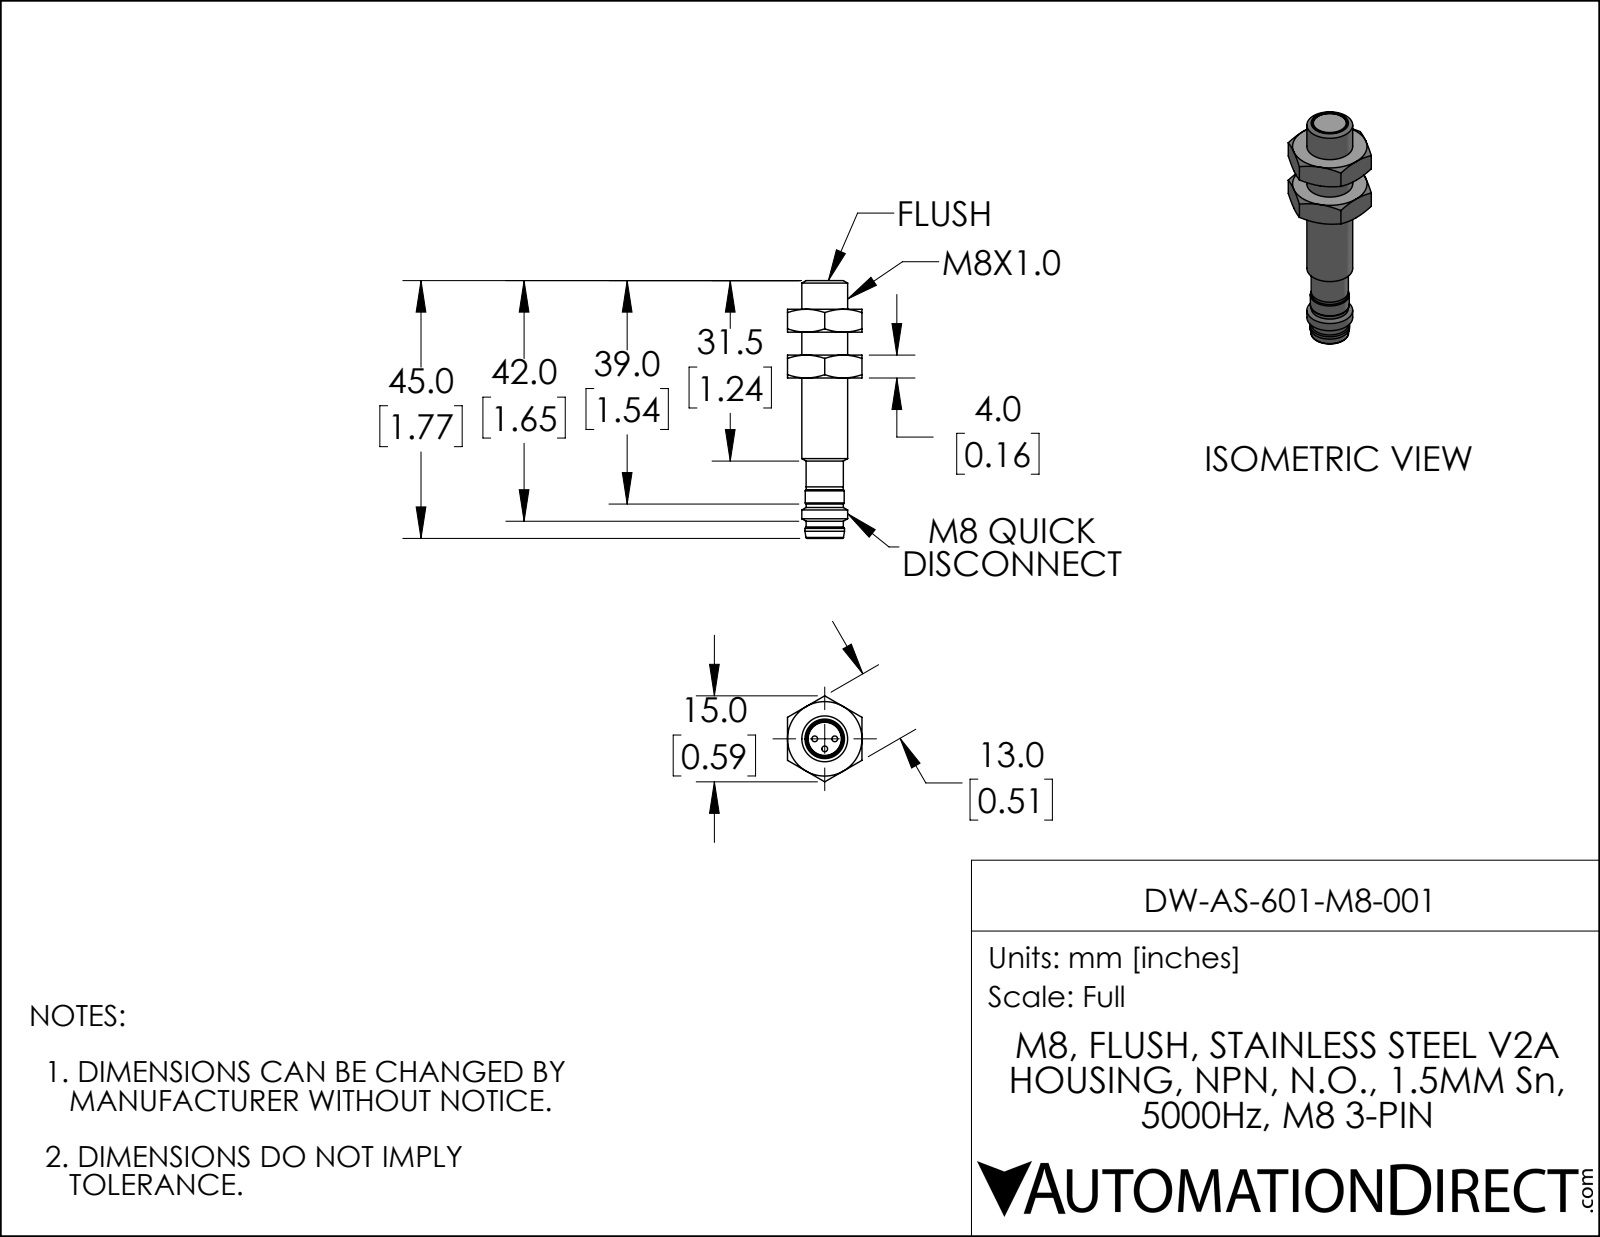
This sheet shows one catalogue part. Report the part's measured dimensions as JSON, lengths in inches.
{"part_name": "DW-AS-601-M8-001", "step_written_by": "SolidWorks 2019 (AUTOMOTIVE_DESIGN)", "units": "inches", "bodies": {"solids": 1, "faces": 77, "planar": 25, "cylindrical": 14, "other": 38}, "overall_size": [1.772, 0.591, 0.512], "volume_in3": 0.165, "surface_area_in2": 2.85, "round_holes": [[0.228, 1]], "round_bosses_or_shafts": [[0.039, 3], [0.315, 1], [0.272, 1], [0.268, 1], [0.256, 1], [0.254, 1]], "face_to_face_distances": [0.157, 0.512, 0.315, 0.472, 0.197, 0.354, 0.669, 1.575, 1.22, 1.063]}
